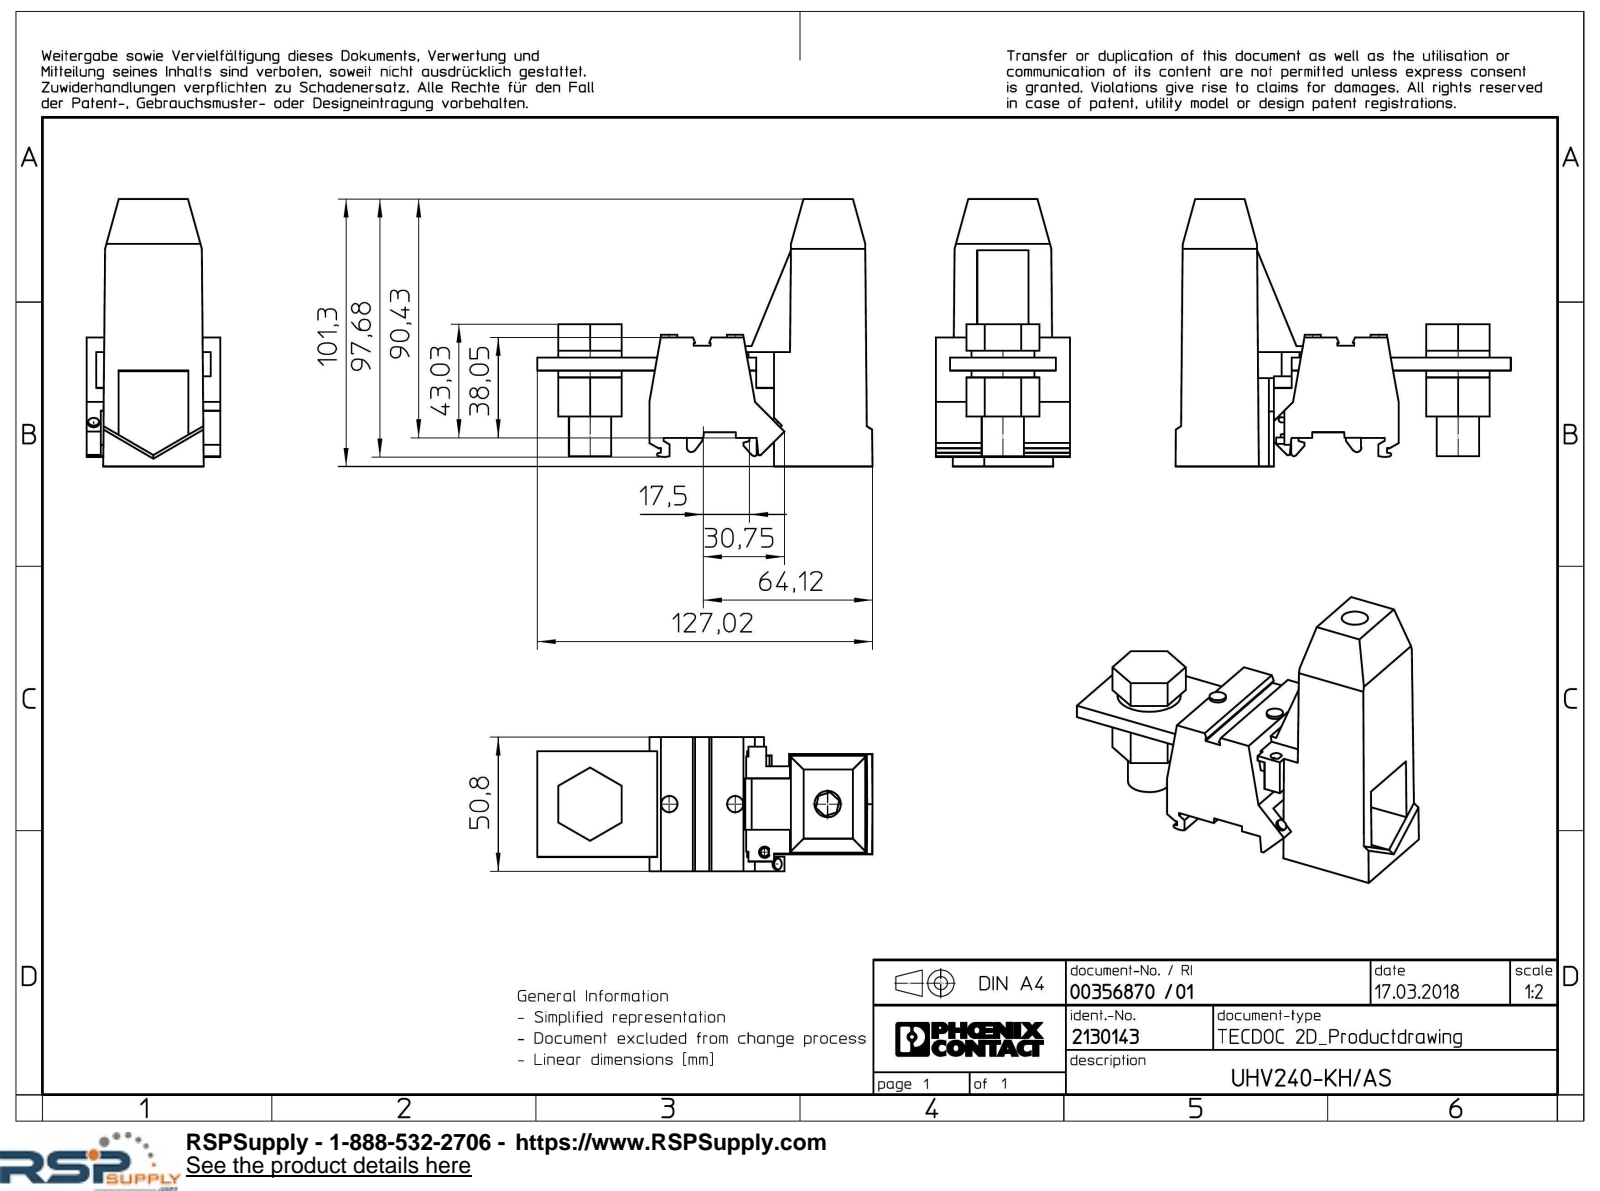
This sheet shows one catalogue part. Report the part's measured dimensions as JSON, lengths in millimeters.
{"part_name": "UHV_240_KH_AS-select", "step_written_by": "Creo Elements/Direct Modeling 18.1I 14-Aug-2016 (C) Parametric Technology GmbH (AUTOMOTIVE_DESIGN)", "units": "millimeters", "bodies": {"solids": 1, "faces": 197, "planar": 174, "cylindrical": 21, "other": 2}, "overall_size": [127.02, 101.3, 50.8], "volume_mm3": 199857, "surface_area_mm2": 42355, "round_holes": [[4.3, 1], [10, 1]], "round_bosses_or_shafts": [[6.2, 2], [24, 1], [16, 1], [4.11, 1]], "partial_cylinders_radius": [[1, 2], [0.3, 1], [0.63, 1], [1.7, 1], [7.2, 1]], "face_to_face_distances": [5, 50.8, 2, 12.15, 38.65, 36.3, 41.3, 48.93, 12.63, 7.63], "hole_center_spacings": [30.02]}
